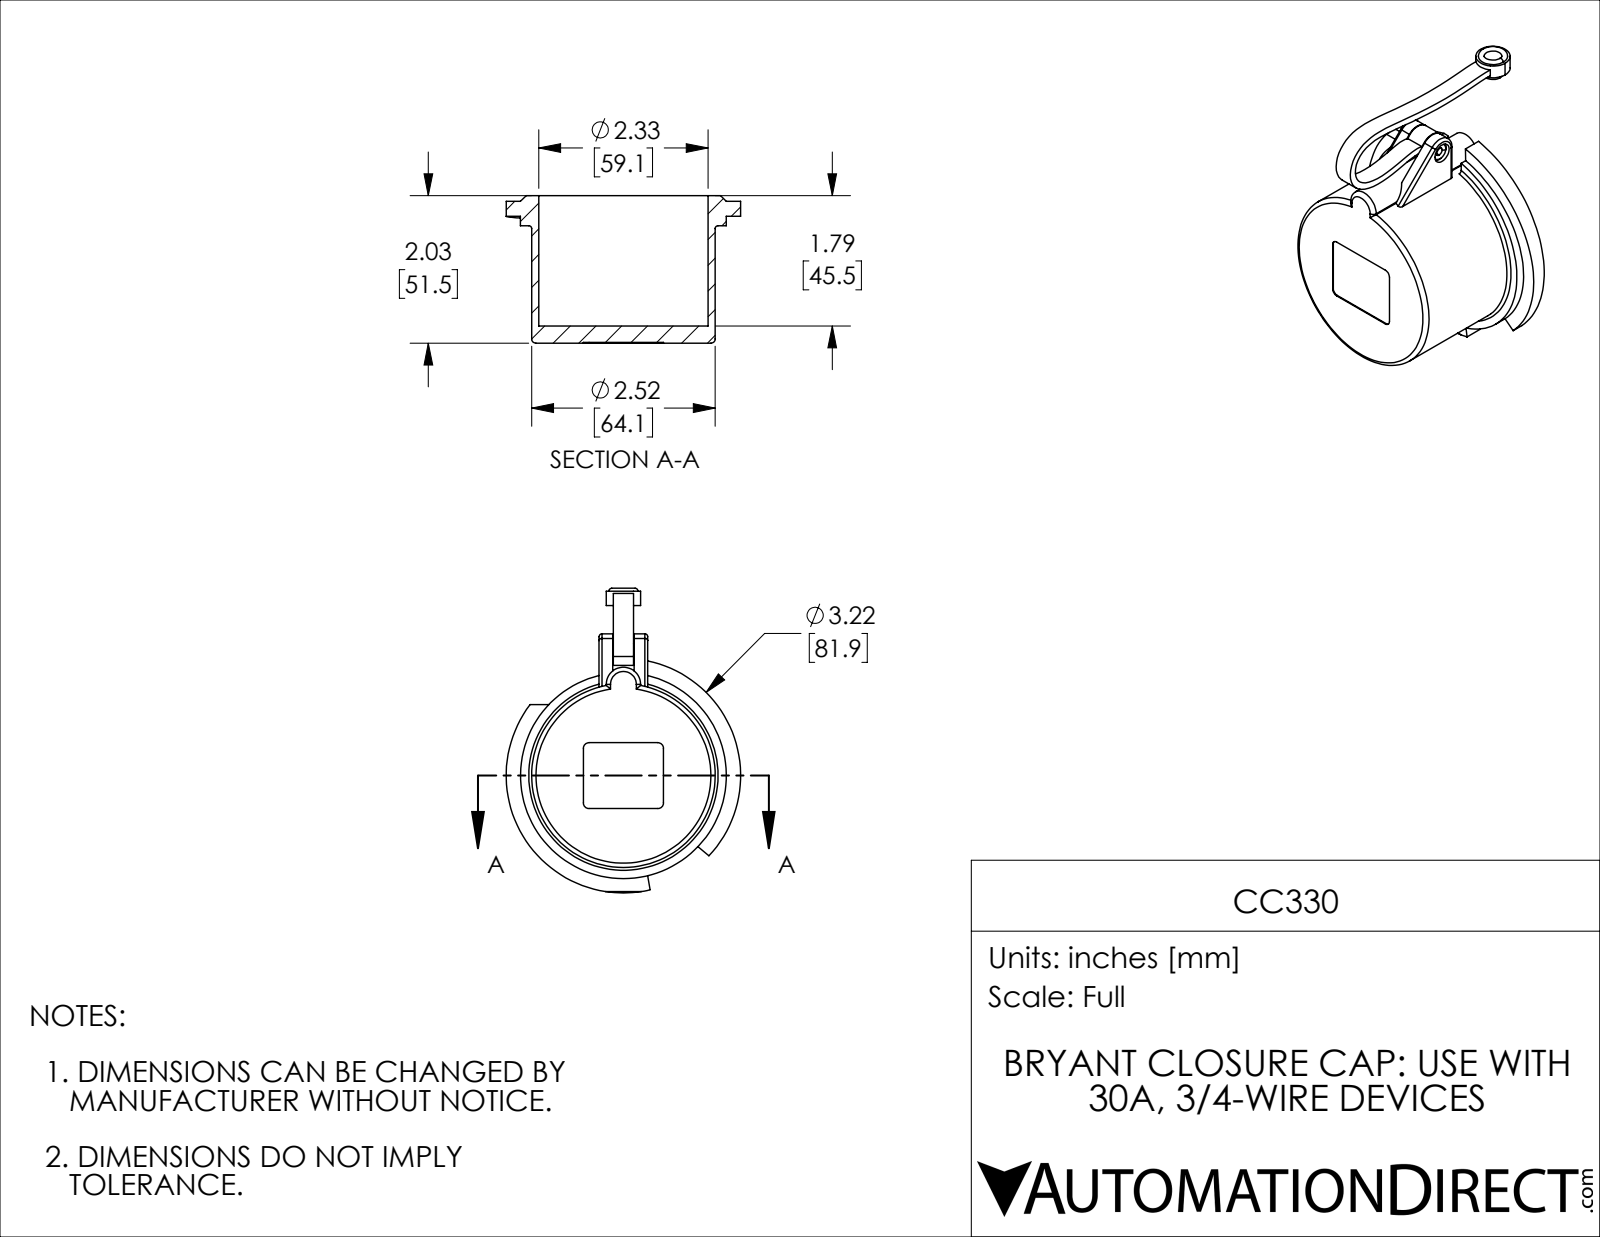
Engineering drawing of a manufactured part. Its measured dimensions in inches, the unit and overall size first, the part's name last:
Units: inches
Overall size (bounding box): 4.187 × 3.224 × 3.149
Round holes (diameter × count): ⌀0.118 ×1, ⌀0.169 ×1, ⌀0.197 ×1, ⌀0.244 ×1, ⌀0.276 ×1, ⌀2.327 ×1
Round bosses / shafts (diameter × count): ⌀2.831 ×1, ⌀2.524 ×1, ⌀0.472 ×1, ⌀0.433 ×1, ⌀0.276 ×1, ⌀0.236 ×1, ⌀0.157 ×1
Partial cylindrical surfaces — rounded edges, fillets, slot ends (radius × count): R0.039 ×4, R0.079 ×4, R0.059 ×2, R0.138 ×1, R0.236 ×1, R1.612 ×1
Main face-to-face distances: 0.236, 1.949, 1.713, 0.079, 2.028, 1.791, 0.224, 1.937, 2.016, 0.413
Volume: 3.681 in³ · Surface area: 52.81 in²
Bodies: 1 solid, 121 faces (42 planar, 58 cylindrical, 21 other)
Part name (STEP PRODUCT): CC330
STEP written by: SolidWorks 2021 (CONFIG_CONTROL_DESIGN)
